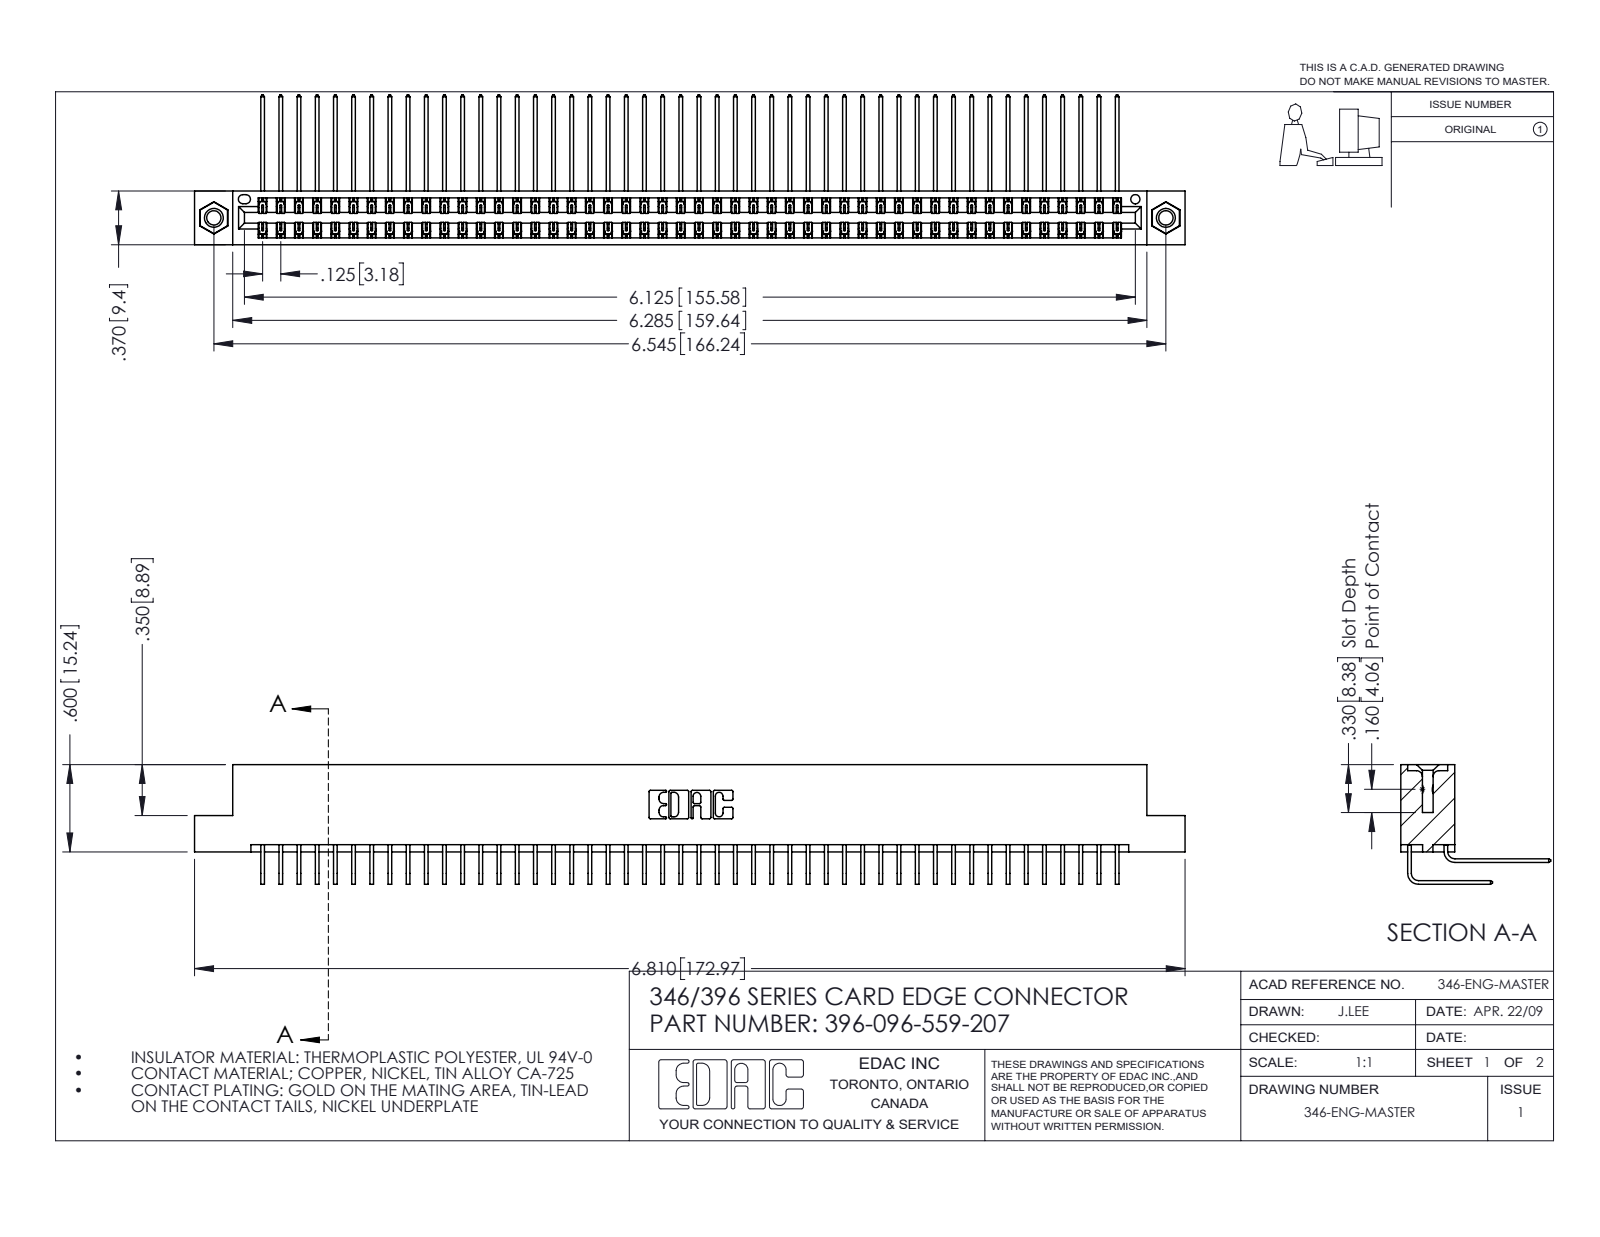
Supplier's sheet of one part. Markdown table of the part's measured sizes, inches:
| quantity | value |
| --- | --- |
| part name | 396-096-559-207; 345-250-001_345-250-005-103; 345-292-001_558 559 Tail - 1; 346 Part_Flush Mounting Lugs - 0.156 Dia-TI (+1 more) |
| STEP written by | SolidWorks 2016 (CONFIG_CONTROL_DESIGN) |
| units | inches |
| bodies | 99 solids, 5366 faces (3660 planar, 1690 cylindrical, 16 other) |
| overall size | 6.81 × 1.03 × 0.823 |
| volume | 1.065 in³ |
| surface area | 41.5 in² |
| round holes (diameter × count) | 0.098 × 2, 0.125 × 2, 0.156 × 2, 0.064 × 1 |
| round bosses / shafts (diameter × count) | 0.155 × 2 |
| partial cylindrical surfaces (radius × count) | 0.006 × 144, 0.01 × 22, 0.007 × 6, 0.031 × 6, 0.026 × 3, 0.014 × 2, 0.022 × 2, 0.024 × 2 |
| main face-to-face distances | 0.048, 0.322, 0.025, 0.37, 0.25, 0.072, 0.298, 0.275, 0.148, 0.222 |
| hole center spacings | 0.246, 6.336, 6.545 |
